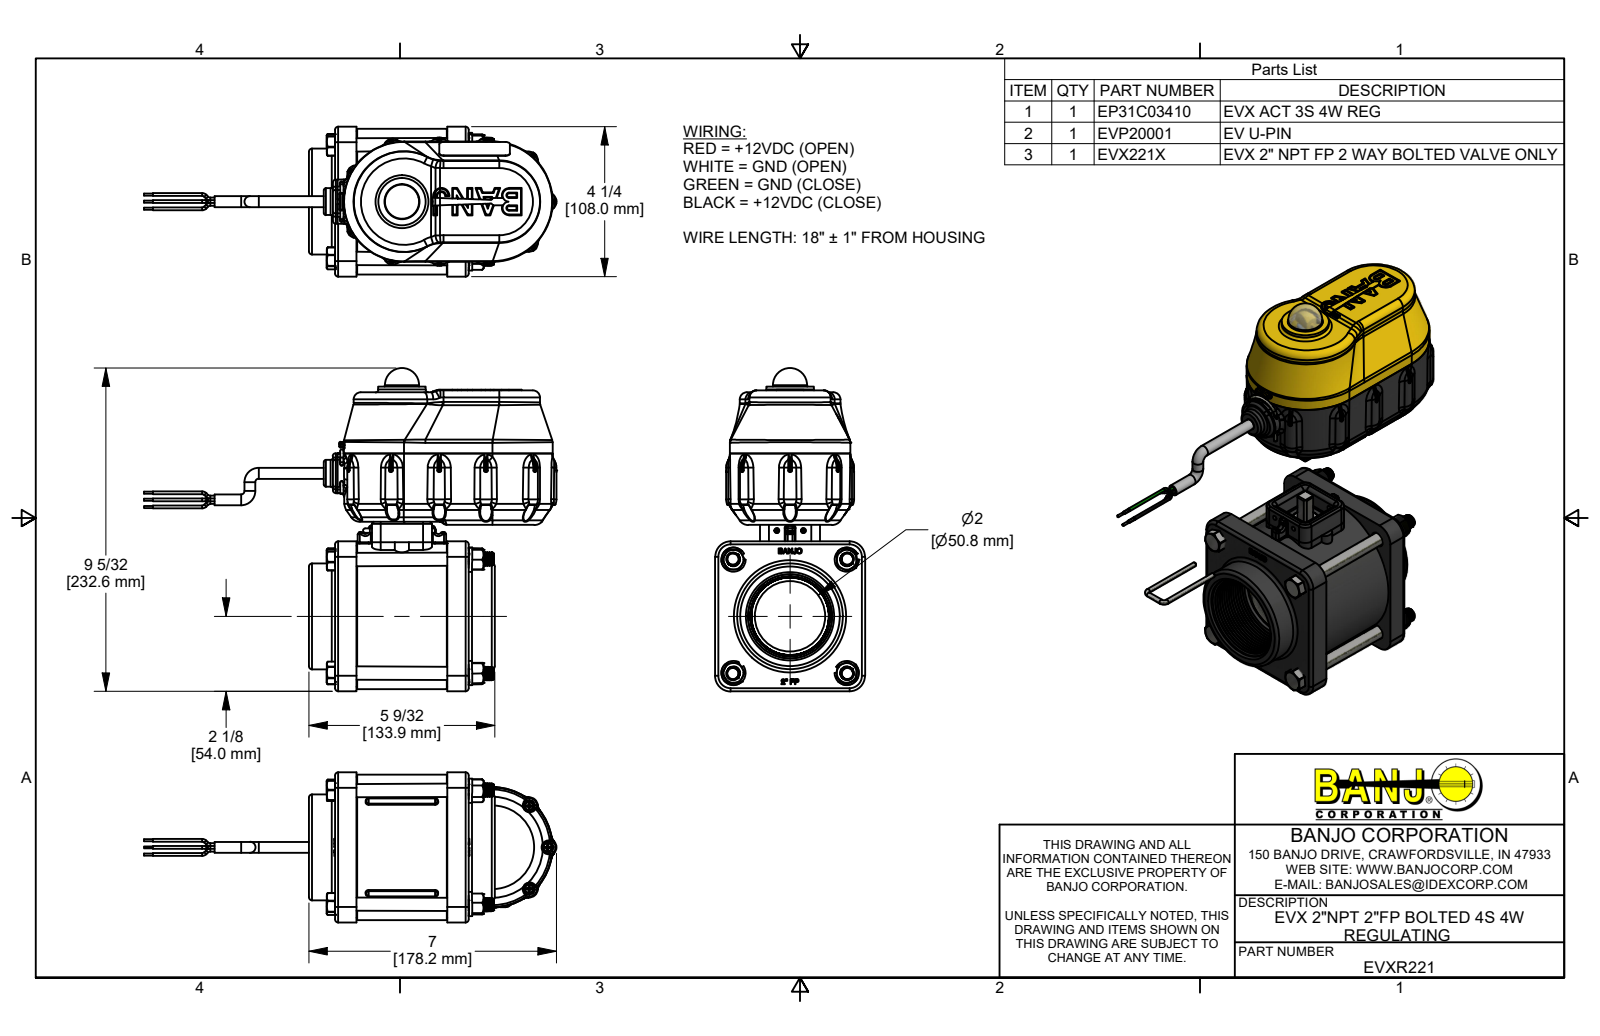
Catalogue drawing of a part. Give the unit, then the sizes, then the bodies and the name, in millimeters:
Units: millimetres
Overall size (bounding box): 296.8 × 232.6 × 108
Round holes (diameter × count): ⌀3.8 ×13, ⌀2.4 ×11, ⌀7.8 ×5, ⌀9.5 ×5, ⌀2.7 ×4, ⌀3.2 ×4, ⌀3.5 ×4, ⌀4.3 ×4, ⌀9.8 ×4, ⌀11.1 ×4, ⌀2.3 ×2, ⌀2.7 ×2
Round bosses / shafts (diameter × count): ⌀8.2 ×60, ⌀2 ×20, ⌀6.4 ×17, ⌀3.6 ×11, ⌀2.7 ×11, ⌀2.2 ×11, ⌀1.5 ×8, ⌀9.5 ×5
Partial cylindrical surfaces — rounded edges, fillets, slot ends (radius × count): R1 ×147, R0.5 ×107, R0.3 ×58, R0.1 ×45, R0.8 ×43, R0.4 ×32, R1.5 ×32, R2 ×28
Main face-to-face distances: 2.5, 65.2, 15.5, 80.8, 17.7, 2.2, 78.6, 63.1, 63.8, 96.3
Hole centre spacings: 57.5, 81.4, 32.6, 75.4, 87.6, 94.9, 107, 12.4
Volume: 1 161 000 mm³ · Surface area: 478 600 mm²
Bodies: 95 solids, 12812 faces (3716 planar, 3355 cylindrical, 5741 other)
Part name (STEP PRODUCT): EVXR221; EVP20001; EVX221X; MEVX25254A (+8 more)
STEP written by: Autodesk Inventor 2021 (AUTOMOTIVE_DESIGN)
